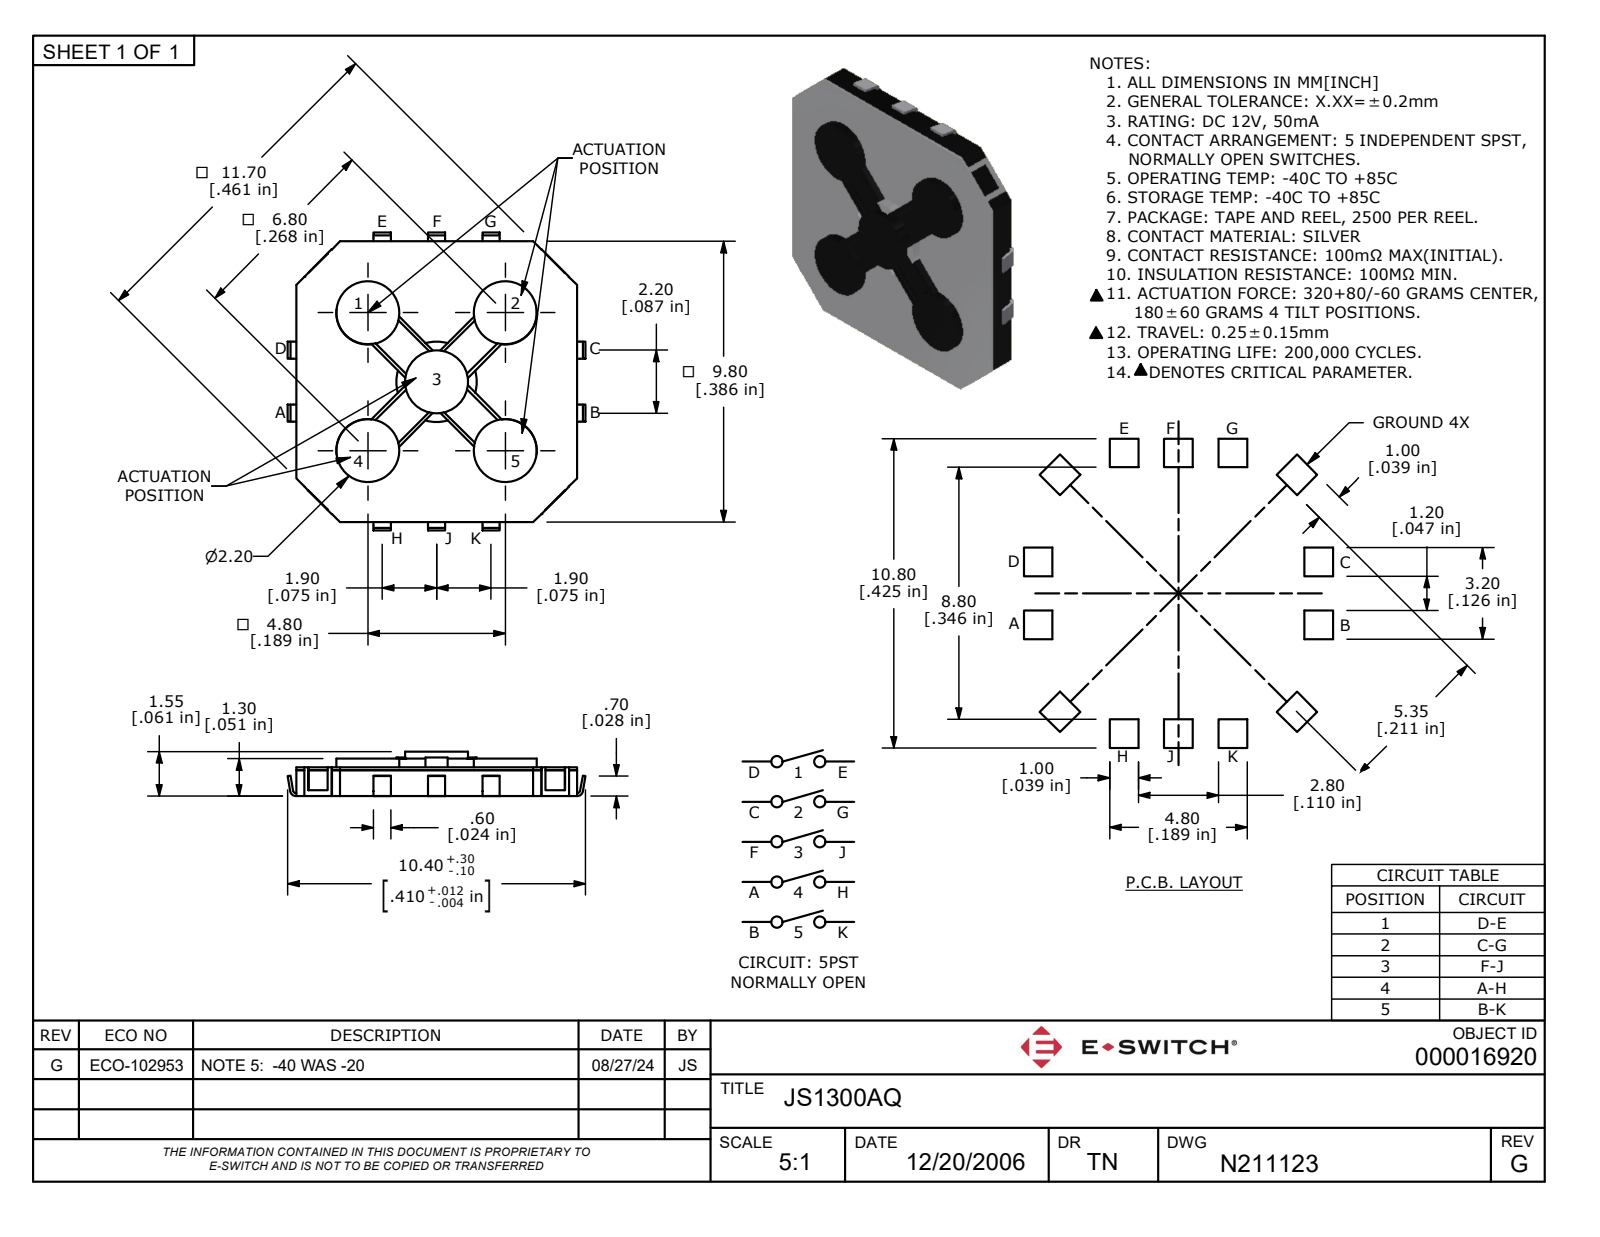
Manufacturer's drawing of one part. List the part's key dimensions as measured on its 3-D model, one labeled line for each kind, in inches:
Part name (STEP PRODUCT): JS1300AQ
STEP written by: Autodesk Inventor 2012 (CONFIG_CONTROL_DESIGN)
Units: inches
Bodies: 1 solid, 274 faces (205 planar, 69 cylindrical, 0 other)
Overall size (bounding box): 0.41 × 0.41 × 0.061
Volume: 0.006 in³ · Surface area: 0.384 in²
Round bosses / shafts (diameter × count): ⌀0.087 ×5
Partial cylindrical surfaces — rounded edges, fillets, slot ends (radius × count): R0.005 ×24, R0.004 ×4, R0.008 ×4, R0.043 ×4, R0.055 ×1
Main face-to-face distances: 0.039, 0.052, 0.012, 0.386, 0.061, 0.022, 0.043, 0.018, 0.461, 0.461
